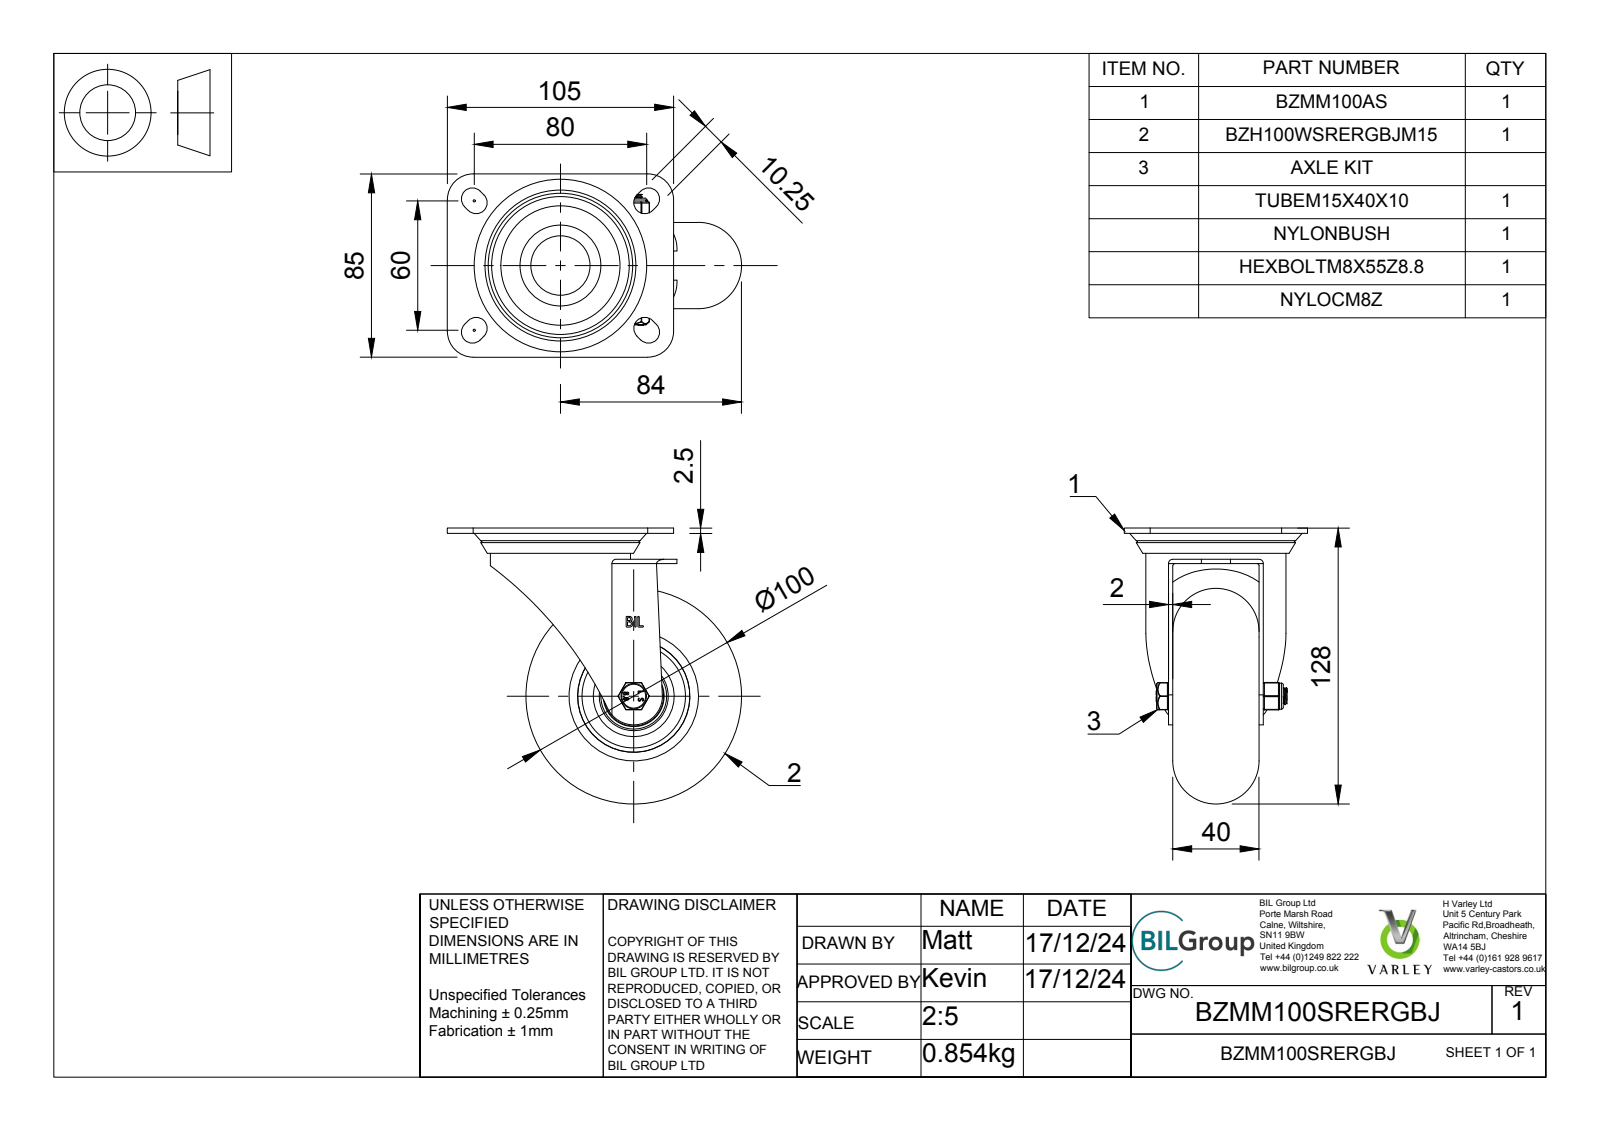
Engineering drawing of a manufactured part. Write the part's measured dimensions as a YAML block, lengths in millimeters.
part_name: "BZMM100SRERGBJ v3; BZMM100AS - 2 v2; ZINC PLATED, PRESSED STEEL TOP PLATE; ZINC PLATED, PRESSED STEEL TOP PLATE Geometry (+7 more)"
step_written_by: "Autodesk Translation Framework v13.20.0.188 (AP242_MANAGED_MODEL_BASED_3D_ENGINEERING_MIM_LF)"
units: millimeters
bodies: {solids: 63, faces: 1122, planar: 371, cylindrical: 211, other: 540}
overall_size: [136.5, 128, 85]
volume: 303125
surface_area: 117458
round_holes:
  - {diameter: 0.66, count: 2}
  - {diameter: 48, count: 2}
  - {diameter: 8, count: 1}
  - {diameter: 8.25, count: 1}
  - {diameter: 8.6, count: 1}
  - {diameter: 10.2, count: 1}
  - {diameter: 15, count: 1}
  - {diameter: 20.5, count: 1}
  - {diameter: 26, count: 1}
  - {diameter: 26.8, count: 1}
  - {diameter: 27.5, count: 1}
  - {diameter: 28, count: 1}
round_bosses_or_shafts:
  - {diameter: 65, count: 1}
  - {diameter: 37.5, count: 1}
  - {diameter: 31.5, count: 1}
  - {diameter: 21.5, count: 1}
  - {diameter: 20, count: 1}
  - {diameter: 19, count: 1}
  - {diameter: 14.95, count: 1}
  - {diameter: 12.1, count: 1}
partial_cylinders:
  - {radius: 0.5, count: 18}
  - {radius: 0.25, count: 12}
  - {radius: 5.12, count: 8}
  - {radius: 0.33, count: 4}
  - {radius: 0.64, count: 4}
  - {radius: 1, count: 4}
  - {radius: 12, count: 4}
  - {radius: 0.63, count: 2}
face_to_face_distances: [2, 2.5, 42, 40, 0.5, 31, 11, 8.6, 8, 14.5]
hole_center_spacings: [3.22, 2.49]
